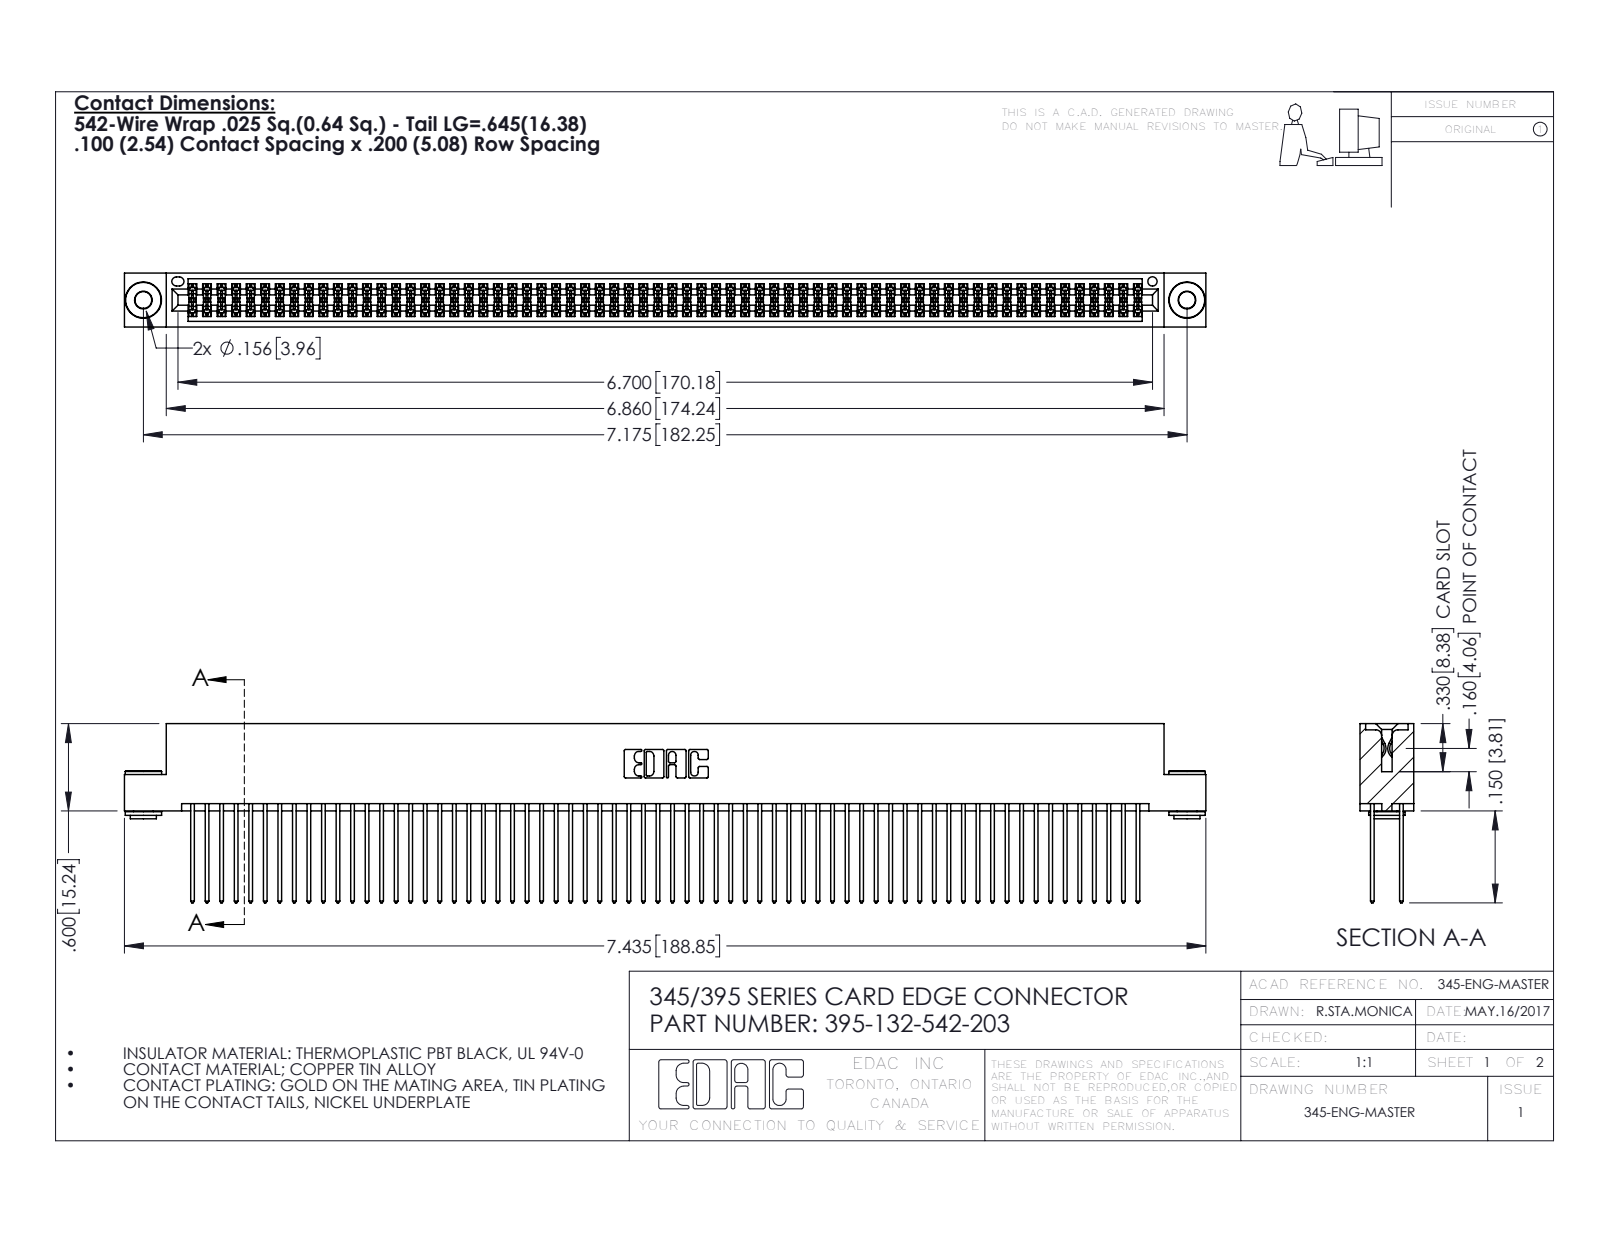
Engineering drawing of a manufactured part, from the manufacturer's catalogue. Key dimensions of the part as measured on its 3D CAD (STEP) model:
Part name (STEP PRODUCT): 395-132-542-203; 345-250-002_345-250-002-102; 345-292-001_345-293-142; 345 Part_Flush Mounting Lugs - 0.156 Dia-TH
STEP written by: SolidWorks 2016 (CONFIG_CONTROL_DESIGN)
Units: inches
Bodies: 135 solids, 6764 faces (4446 planar, 2310 cylindrical, 8 other)
Overall size (bounding box): 7.435 × 1.232 × 0.37
Volume: 1.172 in³ · Surface area: 49.49 in²
Round holes (diameter × count): ⌀0.116 ×2, ⌀0.156 ×2, ⌀0.064 ×1
Round bosses / shafts (diameter × count): ⌀0.25 ×2, ⌀0.18 ×2, ⌀0.136 ×2
Partial cylindrical surfaces — rounded edges, fillets, slot ends (radius × count): R0.006 ×198, R0.01 ×132, R0.01 ×22, R0.007 ×6, R0.031 ×6, R0.026 ×3, R0.014 ×2, R0.019 ×2
Main face-to-face distances: 0.072, 0.298, 0.2, 0.025, 0.098, 0.272, 0.225, 0.37, 0.175, 0.149
Hole centre spacings: 0.27, 6.939, 7.175
